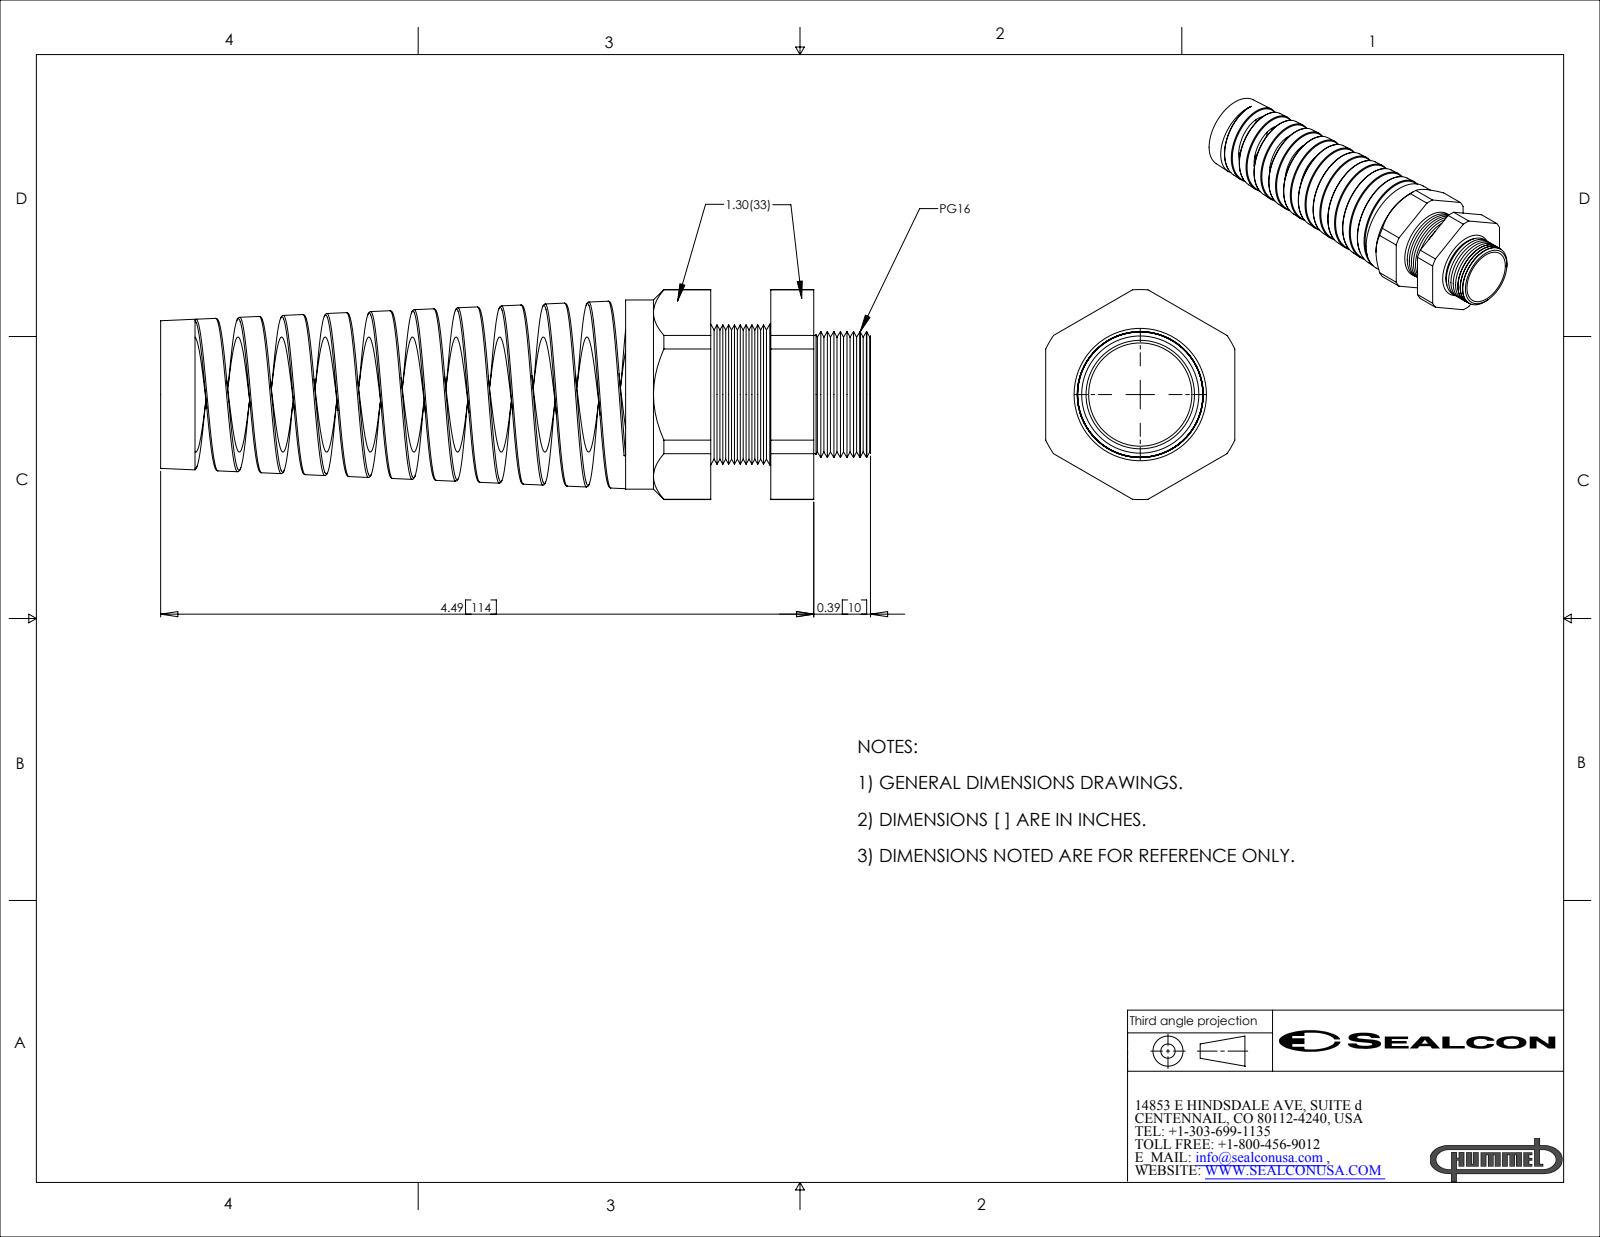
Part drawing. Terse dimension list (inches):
name: CF16GA-GY
written by: SolidWorks 2007 (CONFIG_CONTROL_DESIGN)
unit: in
bodies: 2 solids, 193 faces (24 planar, 45 cylindrical, 124 other)
size: 4.88 × 1.443 × 1.3
volume: 2.002 in³; area: 40.06 in²
holes: 1× ⌀0.71, 1× ⌀0.792
bosses: 1× ⌀1.3, 1× ⌀0.968
rounds: 1× R0.406, 1× R0.721
face distances: 1.3, 0.708, 0.413, 0.295, 0.585, 0.998, 1.294, 3.196, 3.782, 4.195
